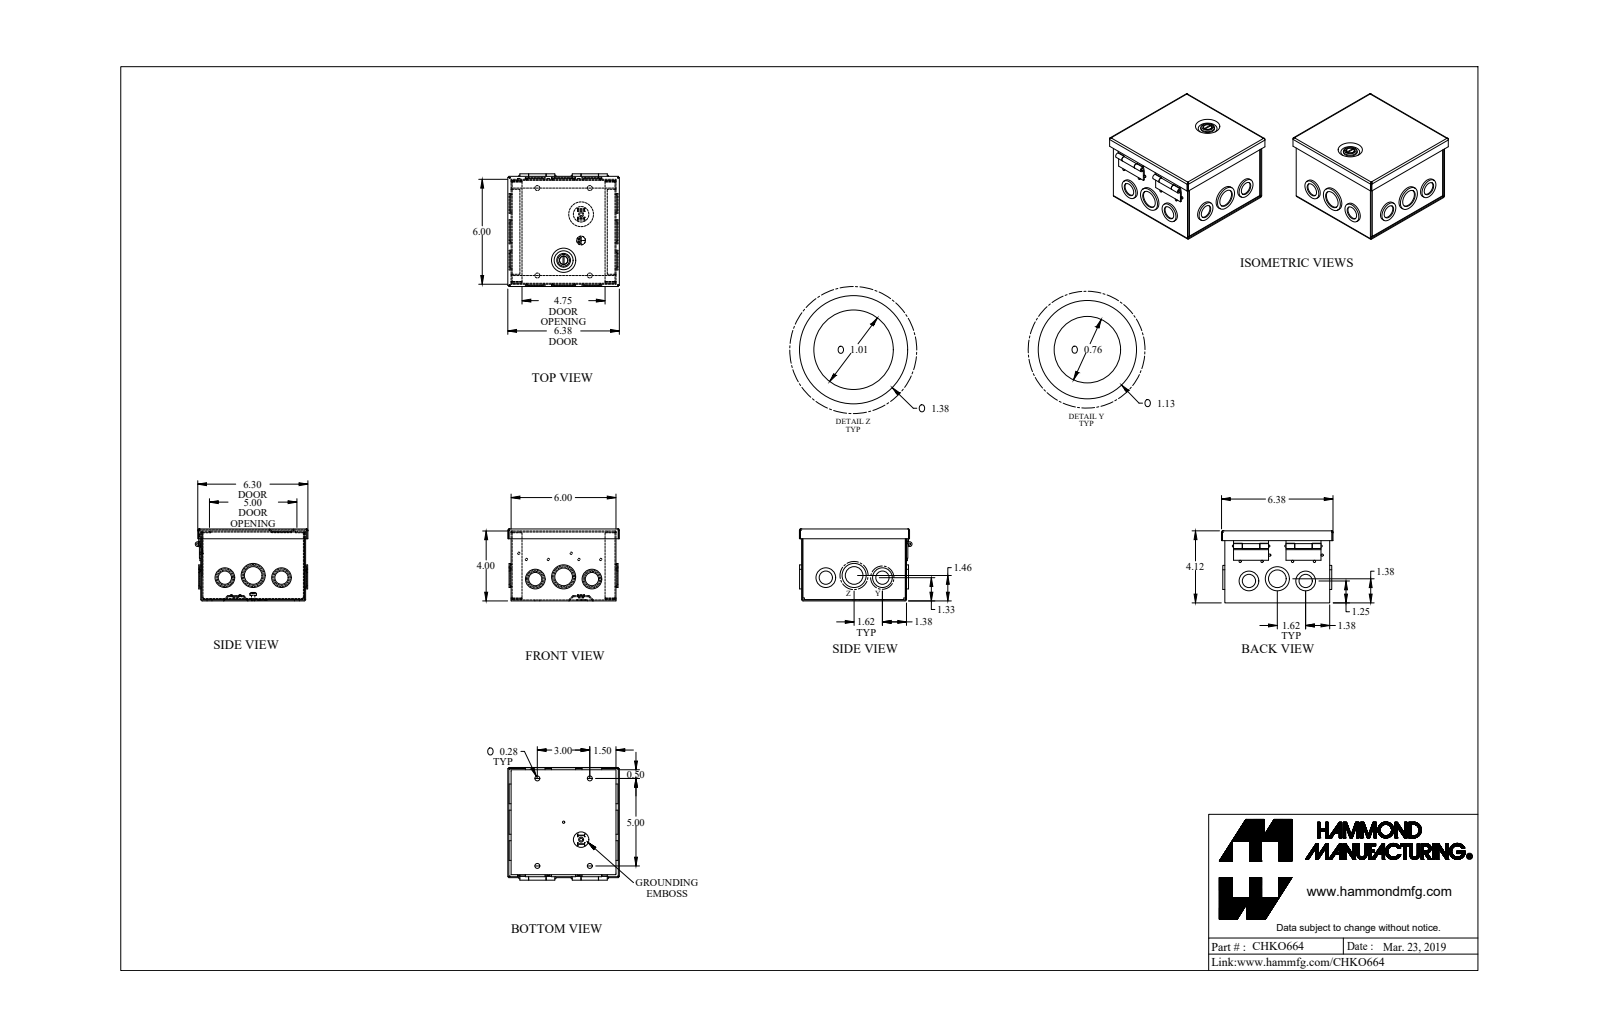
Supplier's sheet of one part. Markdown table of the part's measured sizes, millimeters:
| quantity | value |
| --- | --- |
| part name | CHKO664_Default |
| STEP written by | SolidWorks 2019 (CONFIG_CONTROL_DESIGN) |
| units | millimeters |
| bodies | 12 solids, 631 faces (320 planar, 268 cylindrical, 43 other) |
| overall size | 163.7 × 162.1 × 104.6 |
| volume | 213 500 mm³ |
| surface area | 295 500 mm² |
| round holes (diameter × count) | 25.7 × 6, 7.1 × 4, 19.3 × 4, 32 × 2, 3.2 × 1, 4.3 × 1, 8.1 × 1, 12.1 × 1, 12.7 × 1 |
| round bosses / shafts (diameter × count) | 3.3 × 8, 28.6 × 5, 22.2 × 4, 34.9 × 2, 22.2 × 2, 28.6 × 1, 20 × 1, 13.9 × 1 |
| partial cylindrical surfaces (radius × count) | 0.7 × 16, 2.2 × 16, 1.4 × 8, 0.3 × 4, 2.5 × 4, 0.9 × 2, 2 × 2, 6.4 × 2 |
| main face-to-face distances | 1.4, 151, 103.1, 152.4, 149.5, 104.6, 101.7, 100.2, 3, 1.8 |
| hole center spacings | 41.3, 76.2, 82.3, 127, 148.1, 38.1, 38.3, 40.2 |
